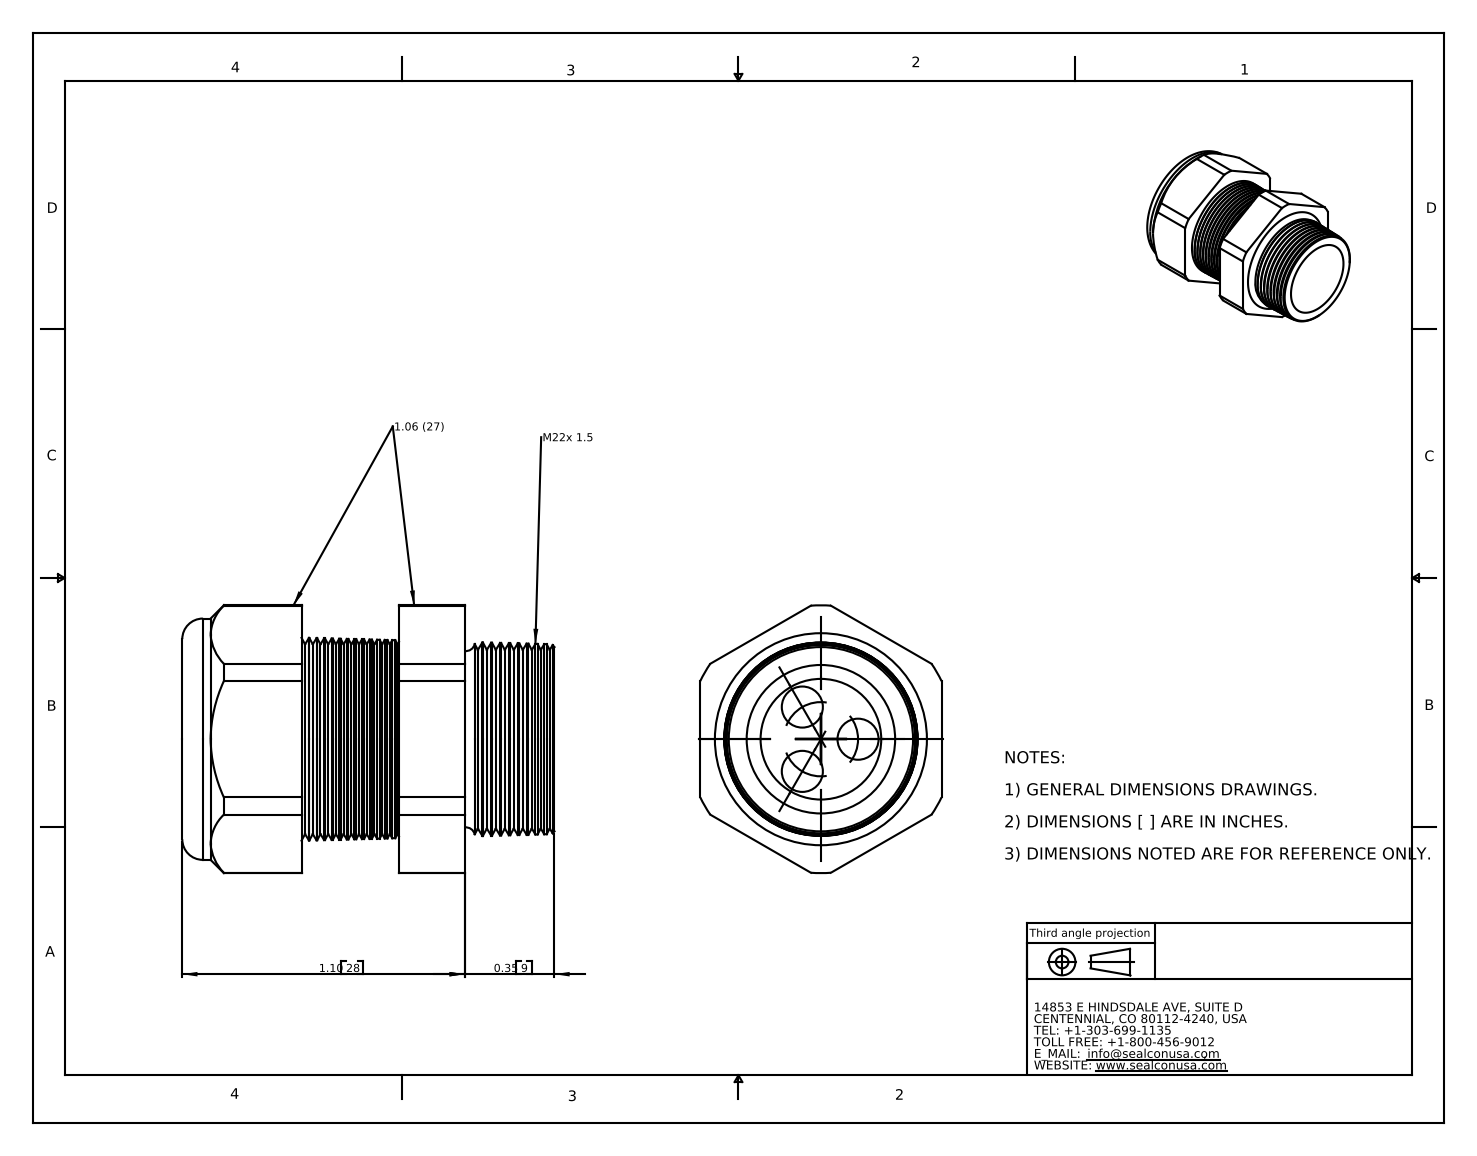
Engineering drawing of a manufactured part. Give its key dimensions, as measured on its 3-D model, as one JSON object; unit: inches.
{"part_name": "CD22M2-GY", "step_written_by": "SolidWorks 2007 (CONFIG_CONTROL_DESIGN)", "units": "inches", "bodies": {"solids": 2, "faces": 192, "planar": 20, "cylindrical": 26, "other": 146}, "overall_size": [1.45, 1.043, 0.94], "volume_in3": 0.581, "surface_area_in2": 10.25, "round_holes": [[0.16, 3], [0.45, 1], [0.47, 1]], "round_bosses_or_shafts": [[0.94, 1]], "partial_cylinders_radius": [[0.522, 1]], "face_to_face_distances": [0.94, 0.844, 0.465, 0.38, 1.1, 0.635, 0.256, 1.45, 0.985, 0.606], "hole_center_spacings": [0.144, 0.25]}
